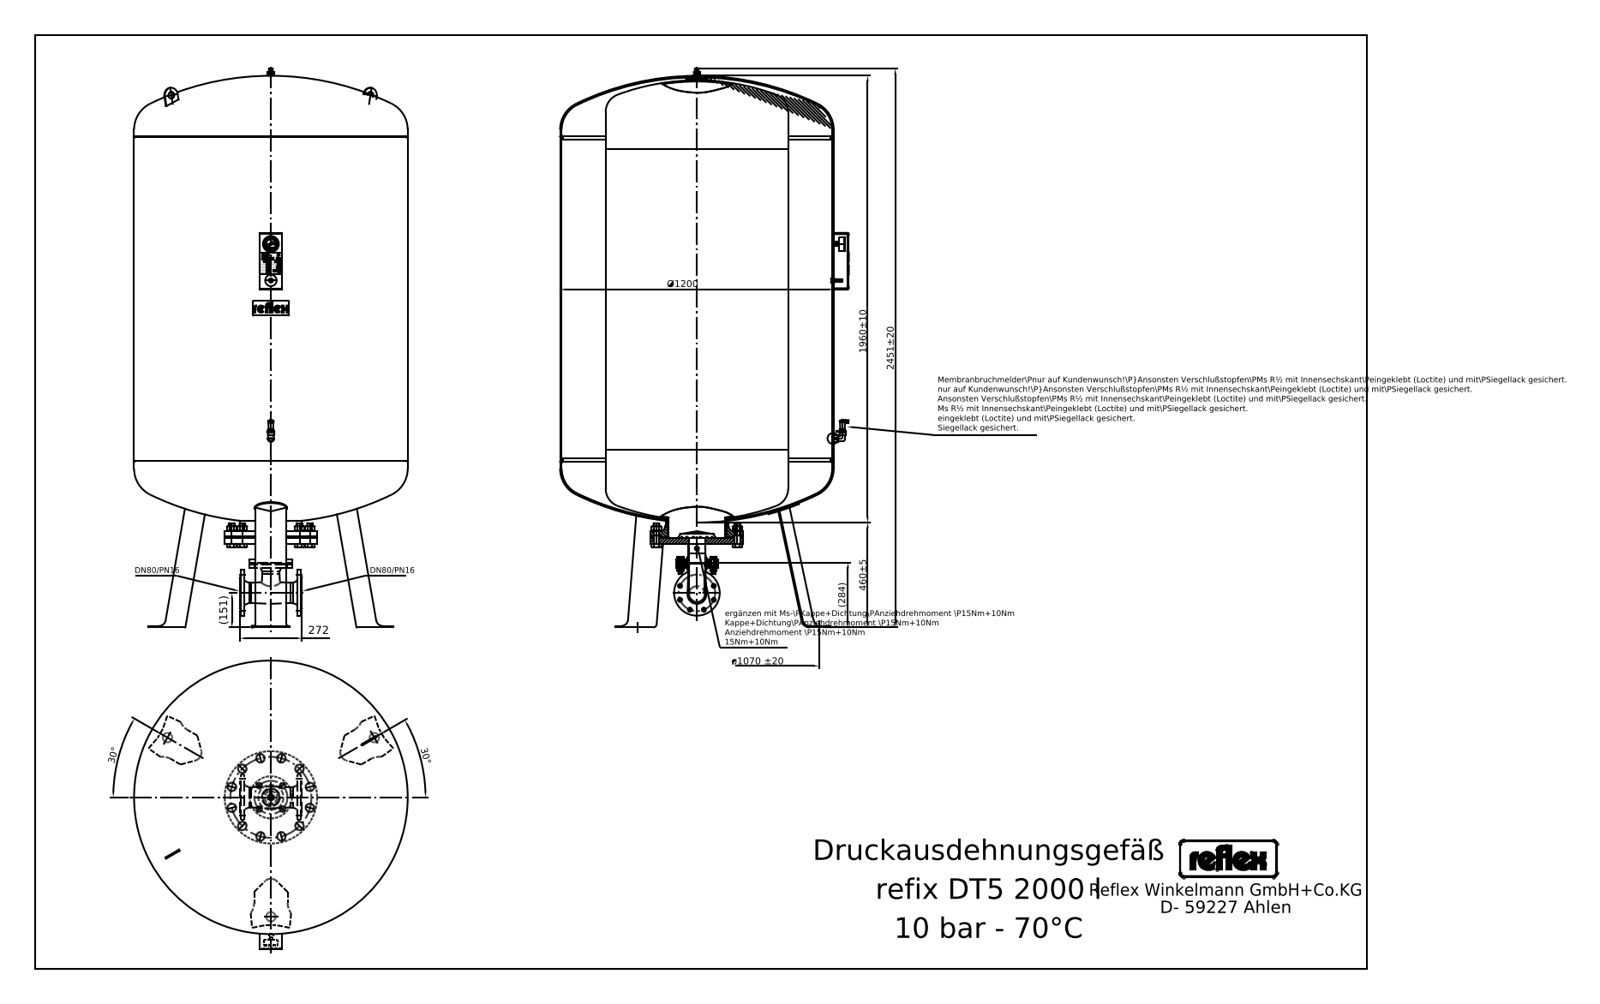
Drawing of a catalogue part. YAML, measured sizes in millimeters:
step_written_by: "Mechanical Desktop 2008 (CONFIG_CONTROL_DESIGN)"
units: millimeters
bodies: {solids: 31, faces: 793, planar: 417, cylindrical: 193, other: 183}
overall_size: [2450, 1266, 1200]
volume: 2046000000
surface_area: 15070000
round_holes:
  - {diameter: 19, count: 8}
  - {diameter: 10, count: 1}
  - {diameter: 30, count: 1}
  - {diameter: 50, count: 1}
  - {diameter: 69, count: 1}
  - {diameter: 88.9, count: 1}
  - {diameter: 260.4, count: 1}
round_bosses_or_shafts:
  - {diameter: 16, count: 17}
  - {diameter: 28, count: 2}
  - {diameter: 26, count: 2}
  - {diameter: 20, count: 2}
  - {diameter: 1200, count: 1}
  - {diameter: 405, count: 1}
  - {diameter: 273, count: 1}
  - {diameter: 200, count: 1}
partial_cylinders:
  - {radius: 25, count: 18}
  - {radius: 5.62, count: 4}
  - {radius: 2.25, count: 3}
  - {radius: 9, count: 3}
  - {radius: 1, count: 2}
  - {radius: 3.84, count: 2}
  - {radius: 5, count: 2}
  - {radius: 6.75, count: 2}
face_to_face_distances: [1450, 26, 312, 1762, 338, 1788, 31, 5.97, 5.89, 57]
hole_center_spacings: [80, 113.13, 61.22, 61.24, 147.81, 147.82, 160, 82.33]
